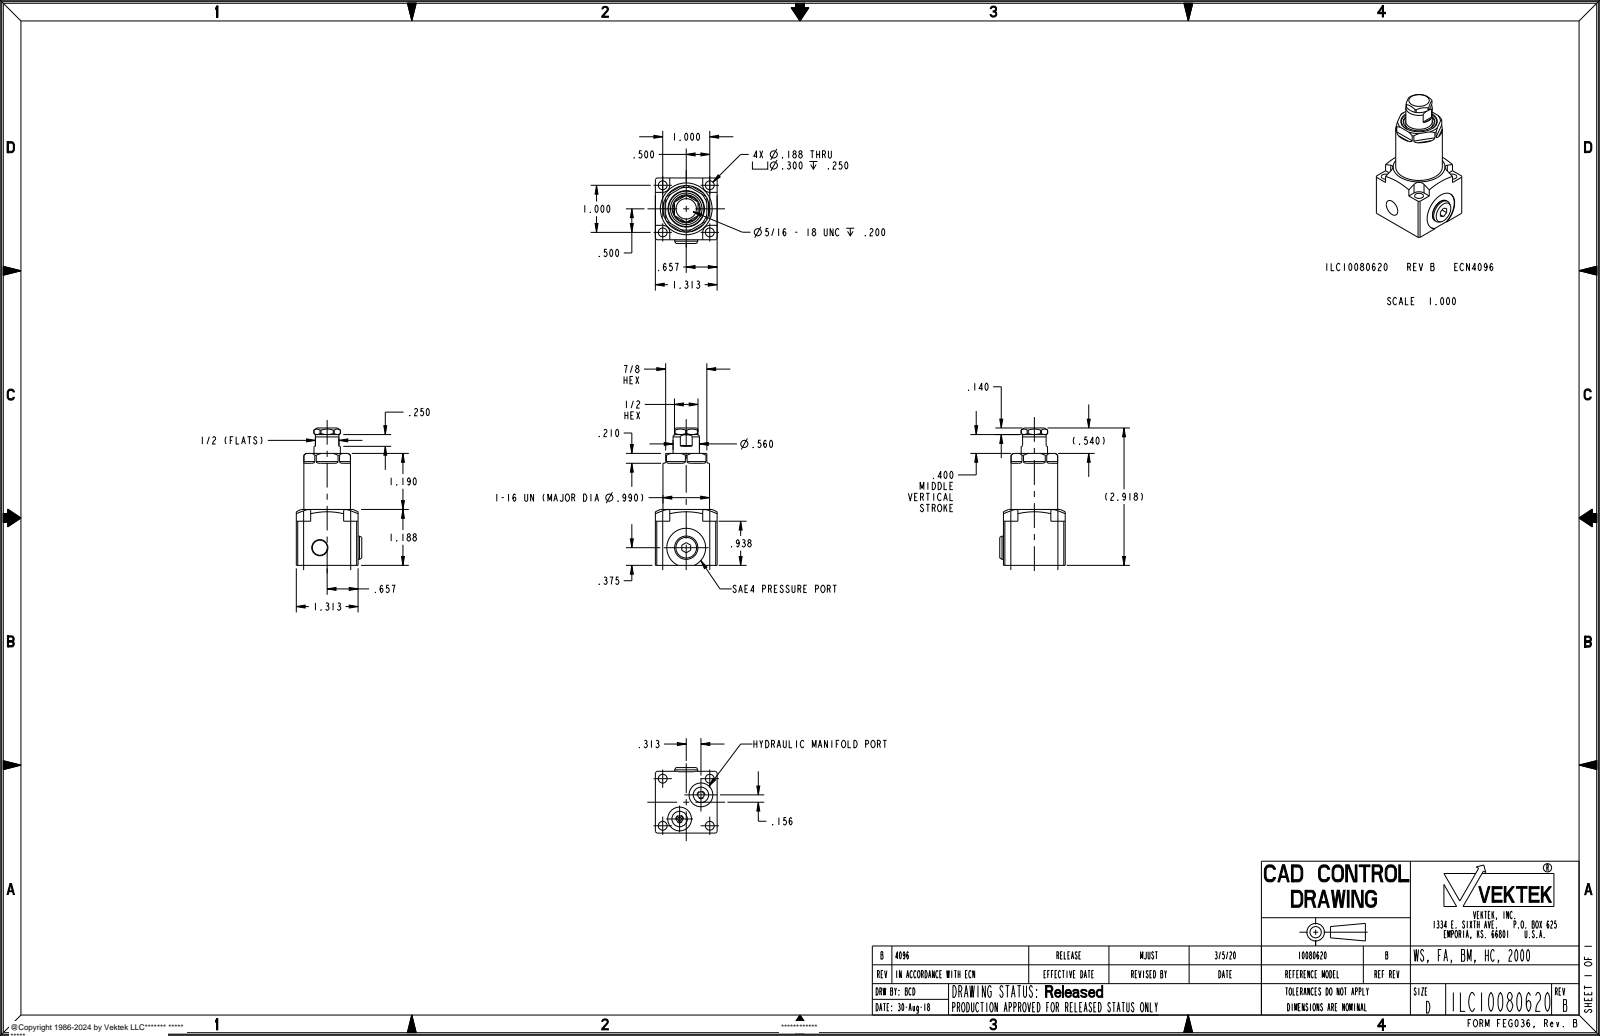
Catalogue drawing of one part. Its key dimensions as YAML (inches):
part_name: "ILC10080620"
step_written_by: "PRO/ENGINEER BY PARAMETRIC TECHNOLOGY CORPORATION, 2017170 (AUTOMOTIVE_DESIGN)"
units: inches
bodies: {solids: 1, faces: 177, planar: 70, cylindrical: 63, other: 44}
overall_size: [2.918, 1.391, 1.313]
volume: 2.704
surface_area: 19.73
round_holes:
  - {diameter: 0.188, count: 4}
  - {diameter: 0.136, count: 2}
  - {diameter: 0.164, count: 2}
  - {diameter: 0.328, count: 2}
  - {diameter: 0.505, count: 2}
  - {diameter: 0.078, count: 1}
  - {diameter: 0.271, count: 1}
  - {diameter: 0.392, count: 1}
  - {diameter: 0.67, count: 1}
  - {diameter: 0.825, count: 1}
round_bosses_or_shafts:
  - {diameter: 0.99, count: 1}
  - {diameter: 0.75, count: 1}
  - {diameter: 0.56, count: 1}
  - {diameter: 0.438, count: 1}
  - {diameter: 0.437, count: 1}
  - {diameter: 0.313, count: 1}
partial_cylinders:
  - {radius: 0.036, count: 6}
  - {radius: 0.15, count: 4}
  - {radius: 0.018, count: 2}
  - {radius: 0.281, count: 1}
face_to_face_distances: [1.313, 1.302, 0.937, 0.187, 0.077, 0.86, 0.875, 0.25, 1.187, 1.11]
hole_center_spacings: [0.707, 1, 1.414, 0.349, 0.383, 0.387, 0.392, 0.657]
